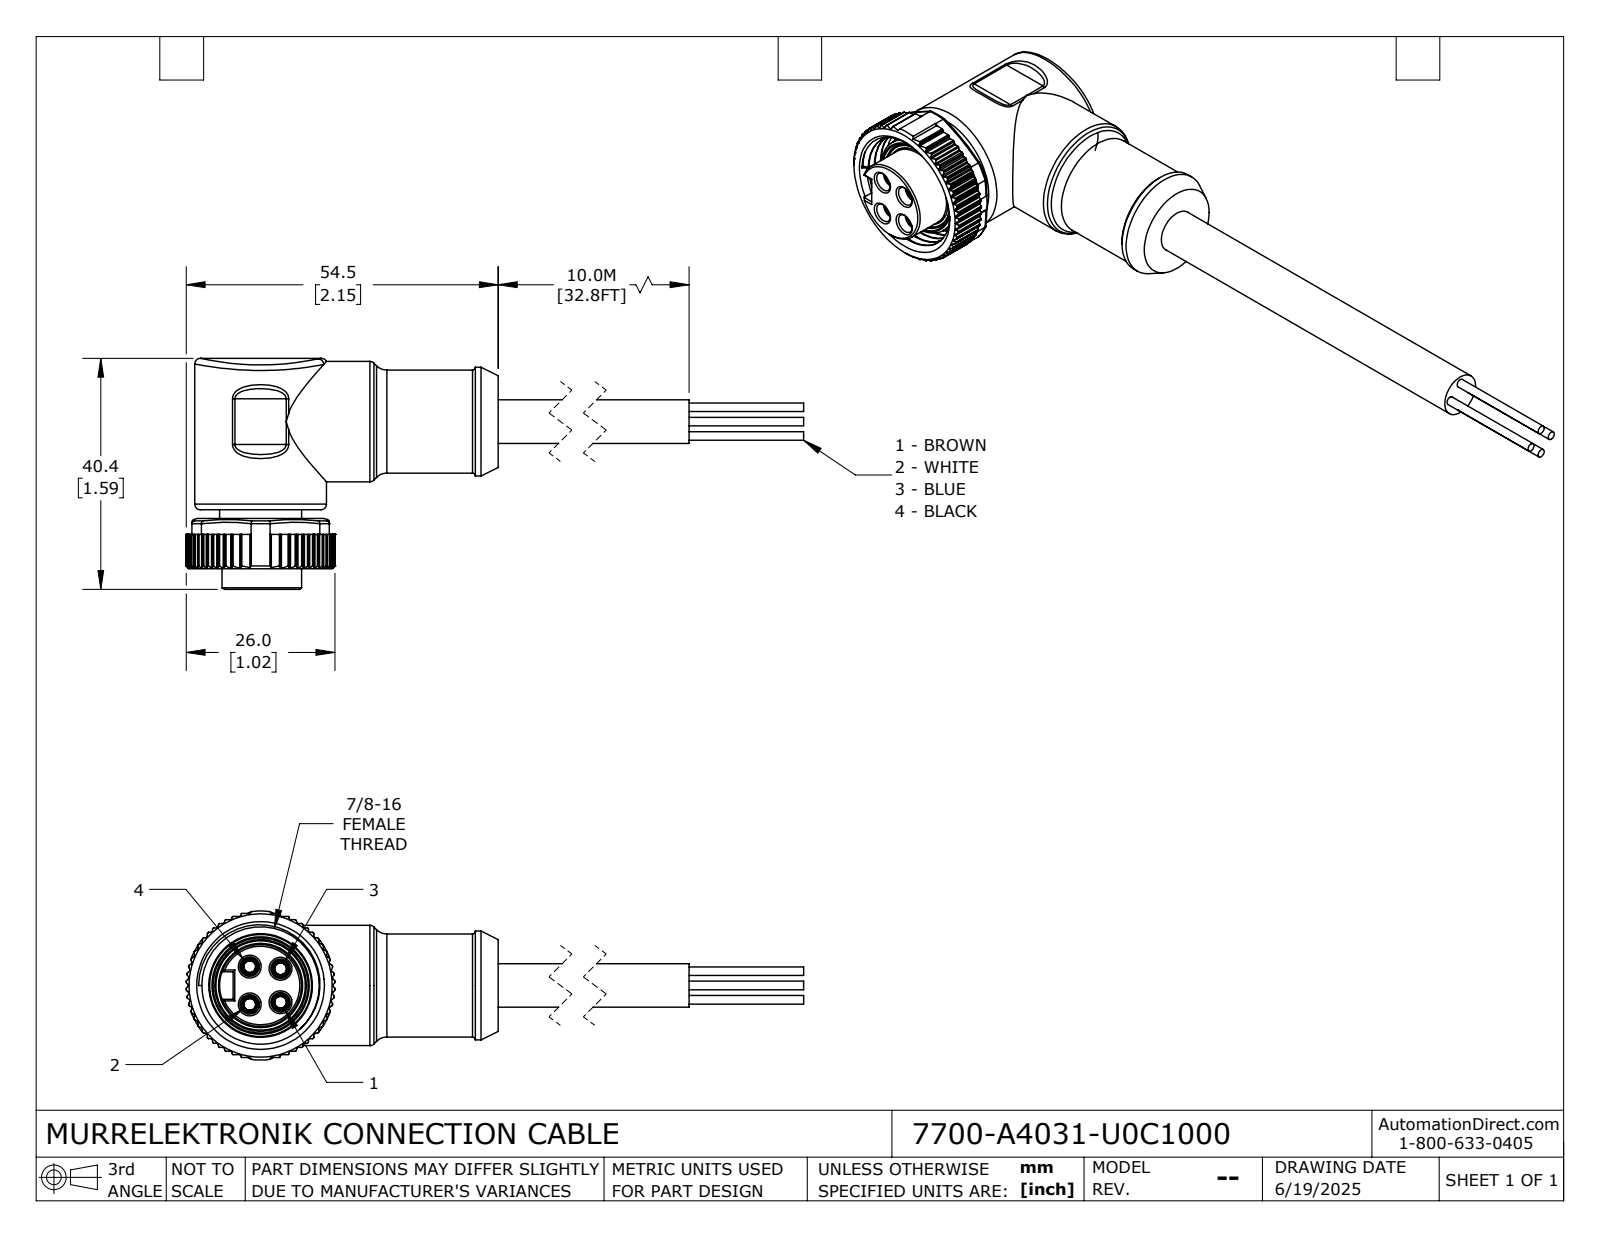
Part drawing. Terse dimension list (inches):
name: 7700-A4031-U0C1000
written by: SolidWorks 2024 (CONFIG_CONTROL_DESIGN)
unit: in
bodies: 1 solid, 700 faces (294 planar, 315 cylindrical, 91 other)
size: 5.689 × 1.589 × 1.024
volume: 1.635 in³; area: 15.26 in²
holes: 4× ⌀0.081, 4× ⌀0.118, 4× ⌀0.134, 1× ⌀0.61, 1× ⌀0.614, 1× ⌀0.807, 1× ⌀0.875
bosses: 4× ⌀0.059, 1× ⌀0.906, 1× ⌀0.827, 1× ⌀0.748, 1× ⌀0.713, 1× ⌀0.709, 1× ⌀0.701, 1× ⌀0.563
rounds: 126× R0.008, 16× R0.012, 4× R0.004, 4× R0.029, 4× R0.039, 4× R0.098, 1× R0.512, 1× R1.969
face distances: 0.059, 0.142, 0.346, 0.406, 0.488, 0.547, 0.287, 0.118, 0.429, 0.827
hole spacings: 0.15, 0.179, 0.212, 0.324, 0.23, 0.26
